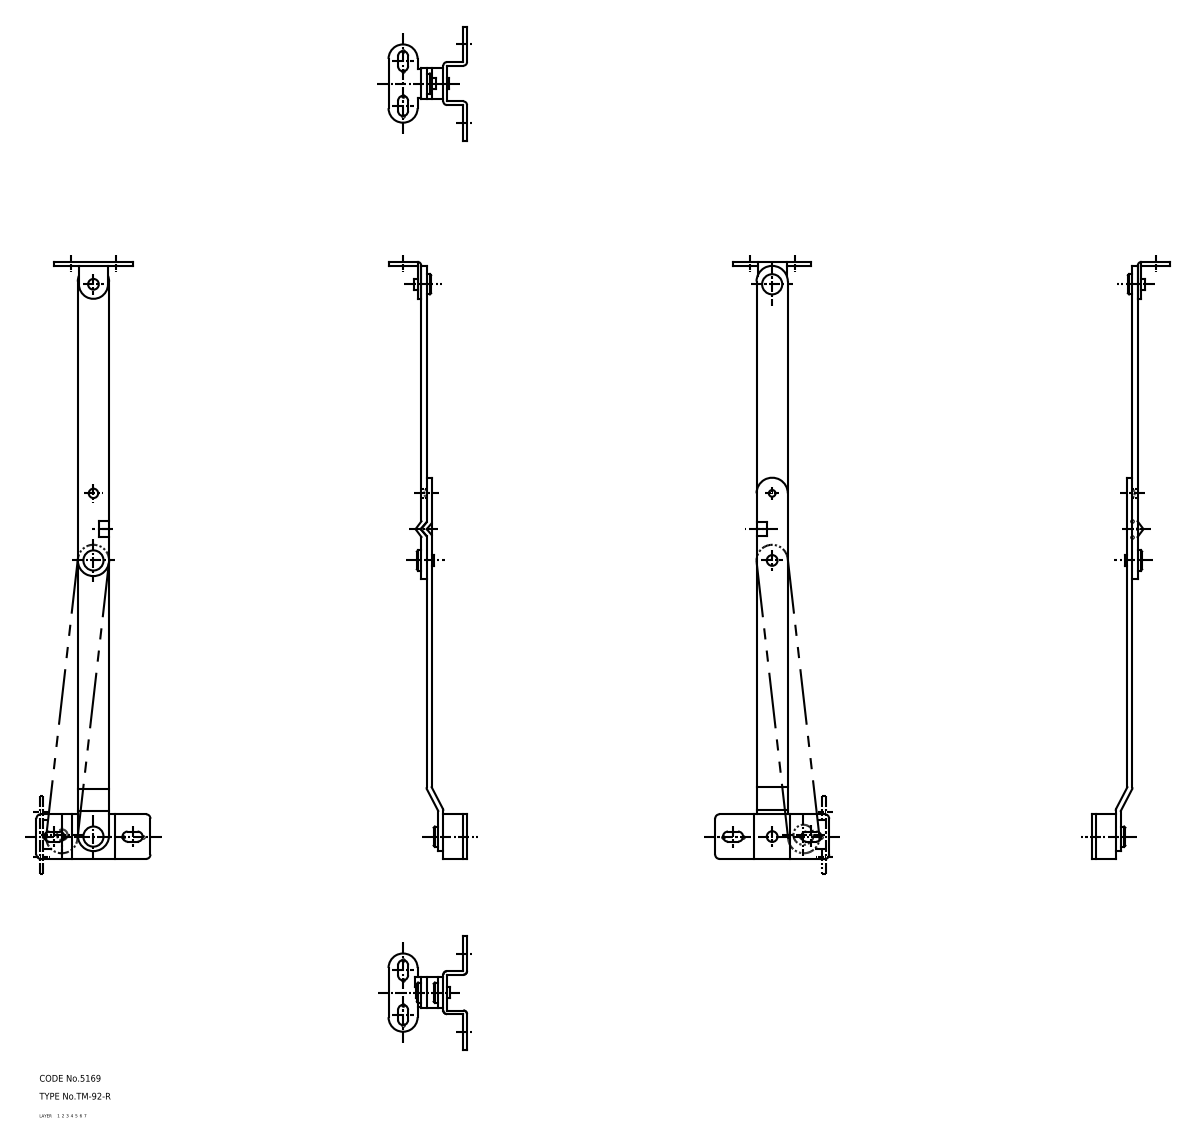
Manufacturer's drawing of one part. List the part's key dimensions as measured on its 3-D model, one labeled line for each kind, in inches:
Part name (STEP PRODUCT): rivet_2_mr-1; rivet_2_mr; rivet_1_mr; bracket_B_mr (+4 more)
STEP written by: CADfix (AUTOMOTIVE_DESIGN)
Units: inches
Bodies: 7 solids, 133 faces (0 planar, 0 cylindrical, 133 other)
Overall size (bounding box): 10.512 × 2.008 × 1.382
Volume: 0.807 in³ · Surface area: 23.73 in²
